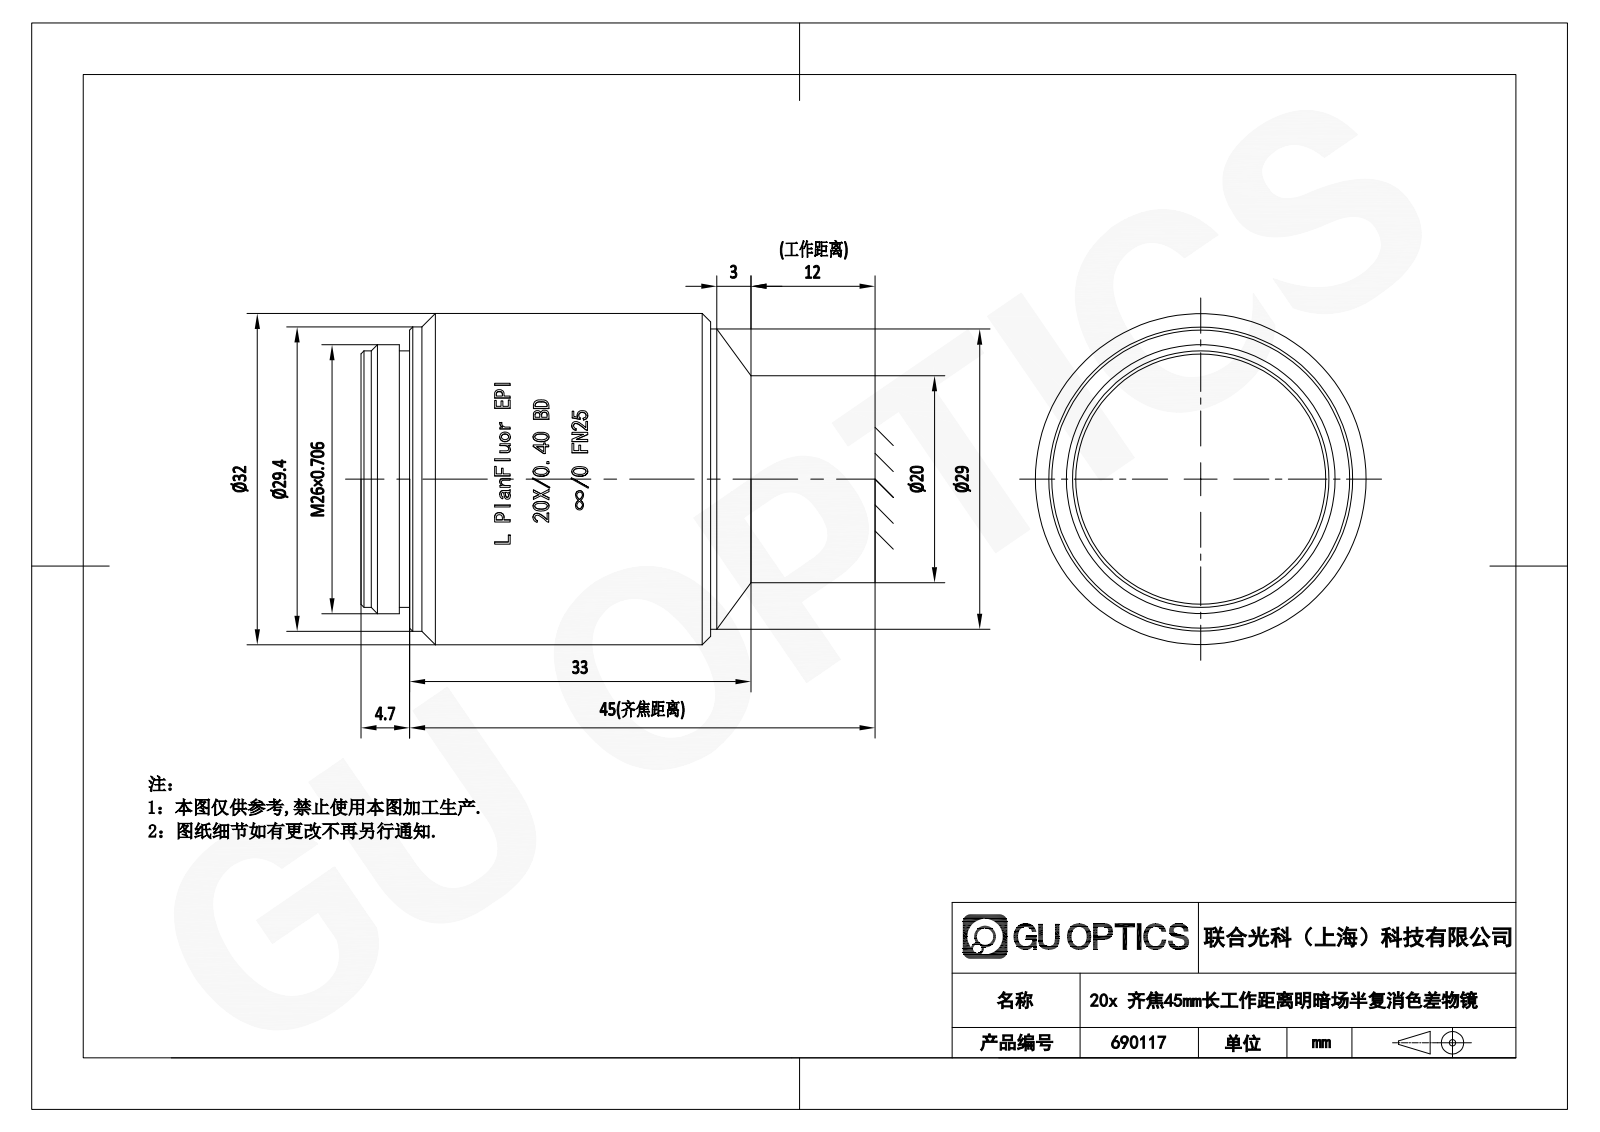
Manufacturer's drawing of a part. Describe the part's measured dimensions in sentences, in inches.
The part is named "690117". Its 3-D file was written by "SolidWorks 2020 (CONFIG_CONTROL_DESIGN)". It is 1 solid with 350 faces: 157 planar, 56 cylindrical and 137 other. Overall it measures 1.484 by 1.262 by 1.26 inches. Its volume is 1.677 cubic inches and its surface area 7.682 square inches. Round bosses or shafts: 1 of diameter 1.26, 1 of diameter 1.157, 1 of diameter 1.142, 1 of diameter 1.024, 1 of diameter 0.976. Partial cylindrical surfaces (rounded edges, fillets, slot ends): 1 of radius 0.632. The main face-to-face distances are 1.484, 0.185, 1.299, 0.154, 1.331, 1.146, 0.146, 0.039, 1.185, 1.339.
